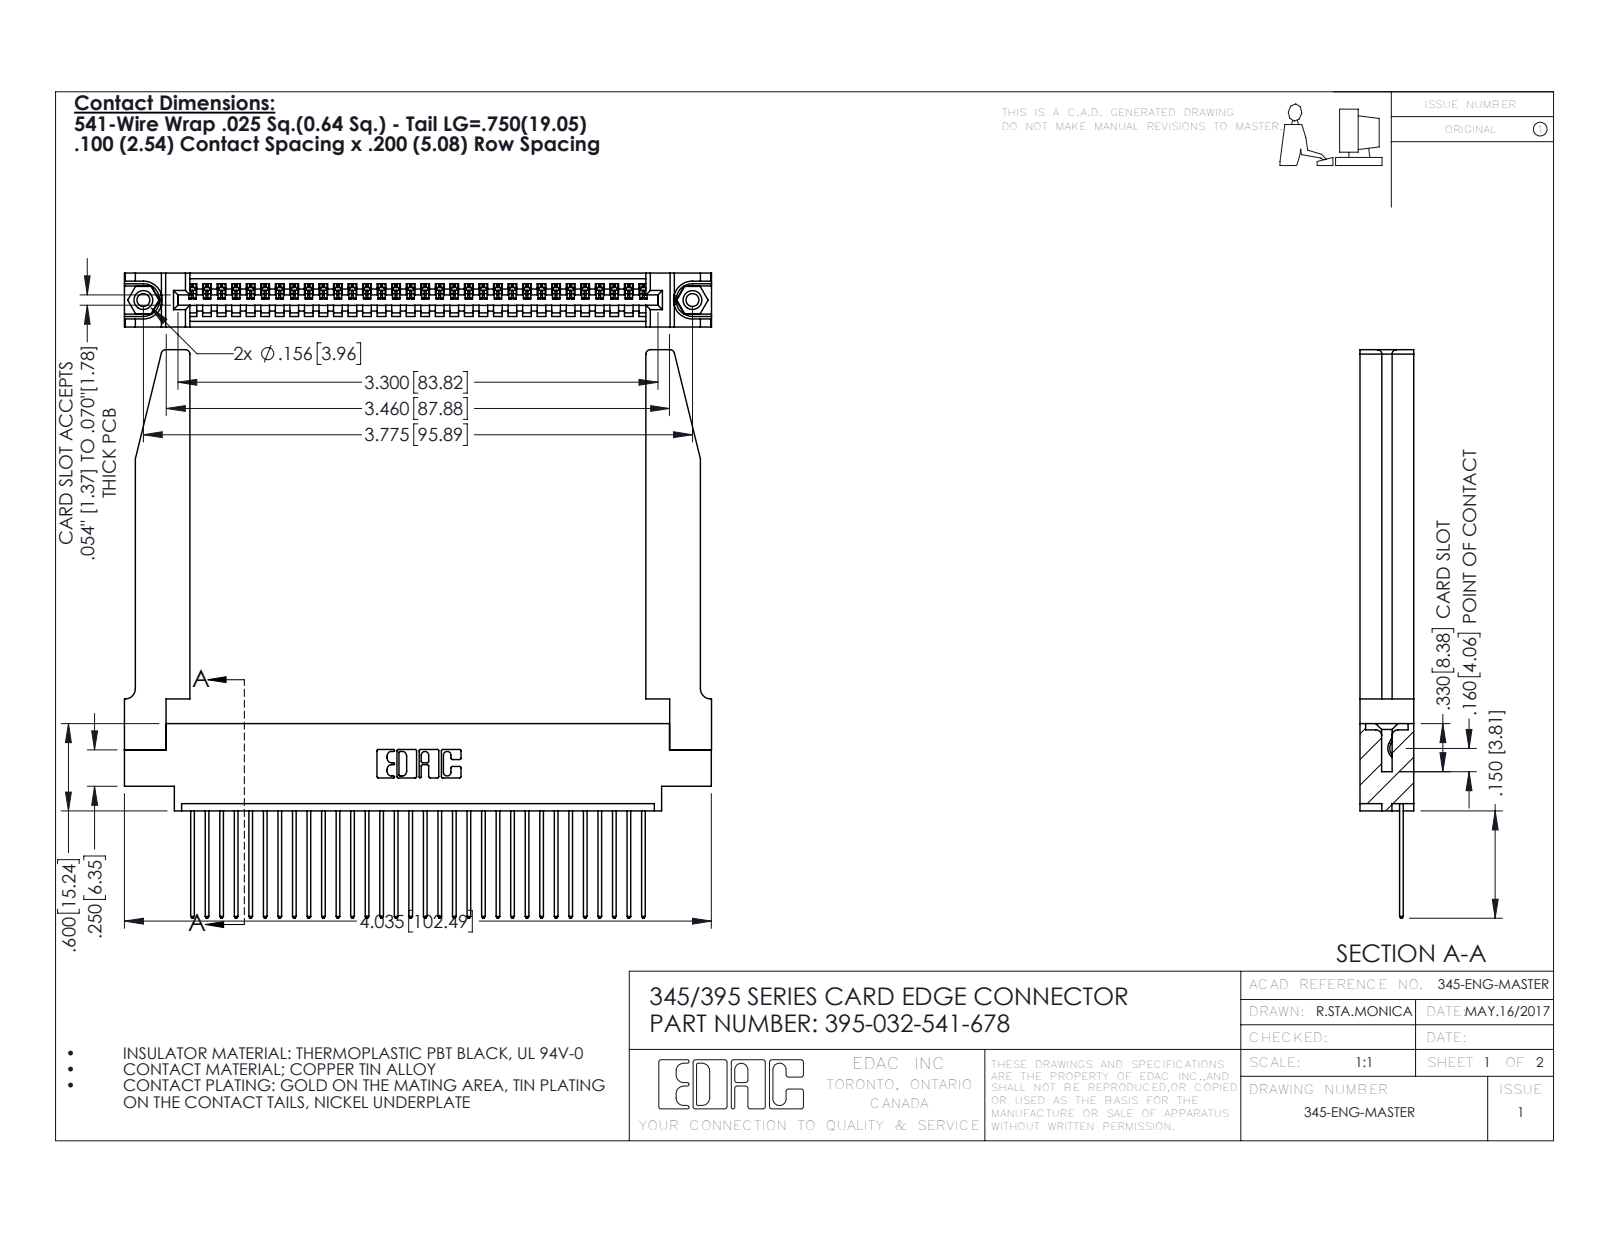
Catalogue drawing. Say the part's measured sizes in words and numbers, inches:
The part is named "345 Part_0.170 Offset - 0.156 Dia-TH; 345-220-078_345-220-078; 345-250-001_345-250-001-102; 395-032-541-678 (+1 more)". Its 3-D file was written by "SolidWorks 2016 (CONFIG_CONTROL_DESIGN)". It is 37 solids with 2220 faces: 1506 planar, 662 cylindrical and 52 other. Overall it measures 4.036 by 3.907 by 0.37 inches. Its volume is 1.063 cubic inches and its surface area 31.43 square inches. Round holes: 2 of diameter 0.089, 2 of diameter 0.125, 2 of diameter 0.156, 1 of diameter 0.064. Round bosses or shafts: 2 of diameter 0.155. Partial cylindrical surfaces (rounded edges, fillets, slot ends): 64 of radius 0.006, 64 of radius 0.01, 22 of radius 0.01, 8 of radius 0.03, 6 of radius 0.007, 6 of radius 0.031, 3 of radius 0.026, 2 of radius 0.031. The main face-to-face distances are 0.37, 0.072, 0.298, 0.098, 0.272, 0.025, 0.2, 0.148, 0.15, 0.225. The hole center spacings are 0.27, 3.54, 3.775.
